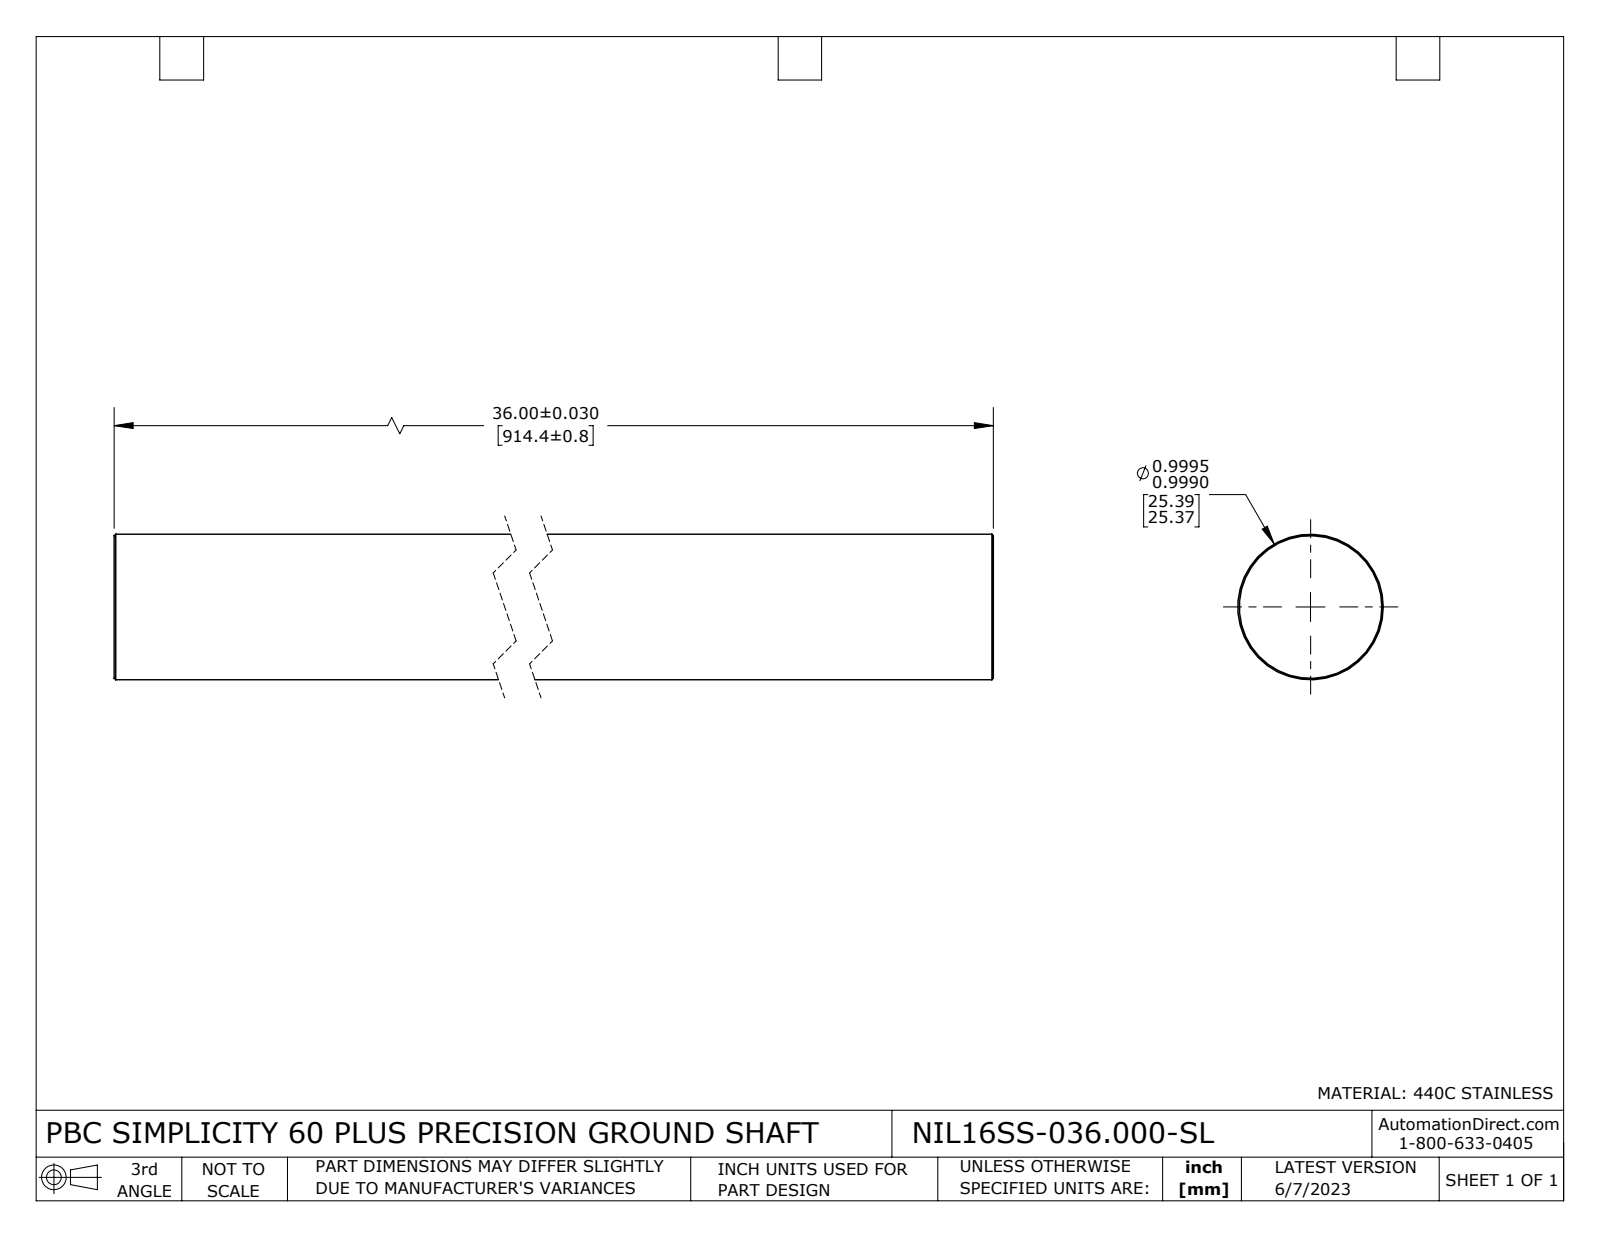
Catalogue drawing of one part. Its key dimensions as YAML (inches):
part_name: "NIL16SS-036.000-SL"
step_written_by: "SolidWorks 2021 (CONFIG_CONTROL_DESIGN)"
units: inches
bodies: {solids: 1, faces: 8, planar: 2, cylindrical: 2, other: 4}
overall_size: [36, 1, 1]
volume: 28.27
surface_area: 114.6
round_bosses_or_shafts:
  - {diameter: 1, count: 1}
face_to_face_distances: [36]
